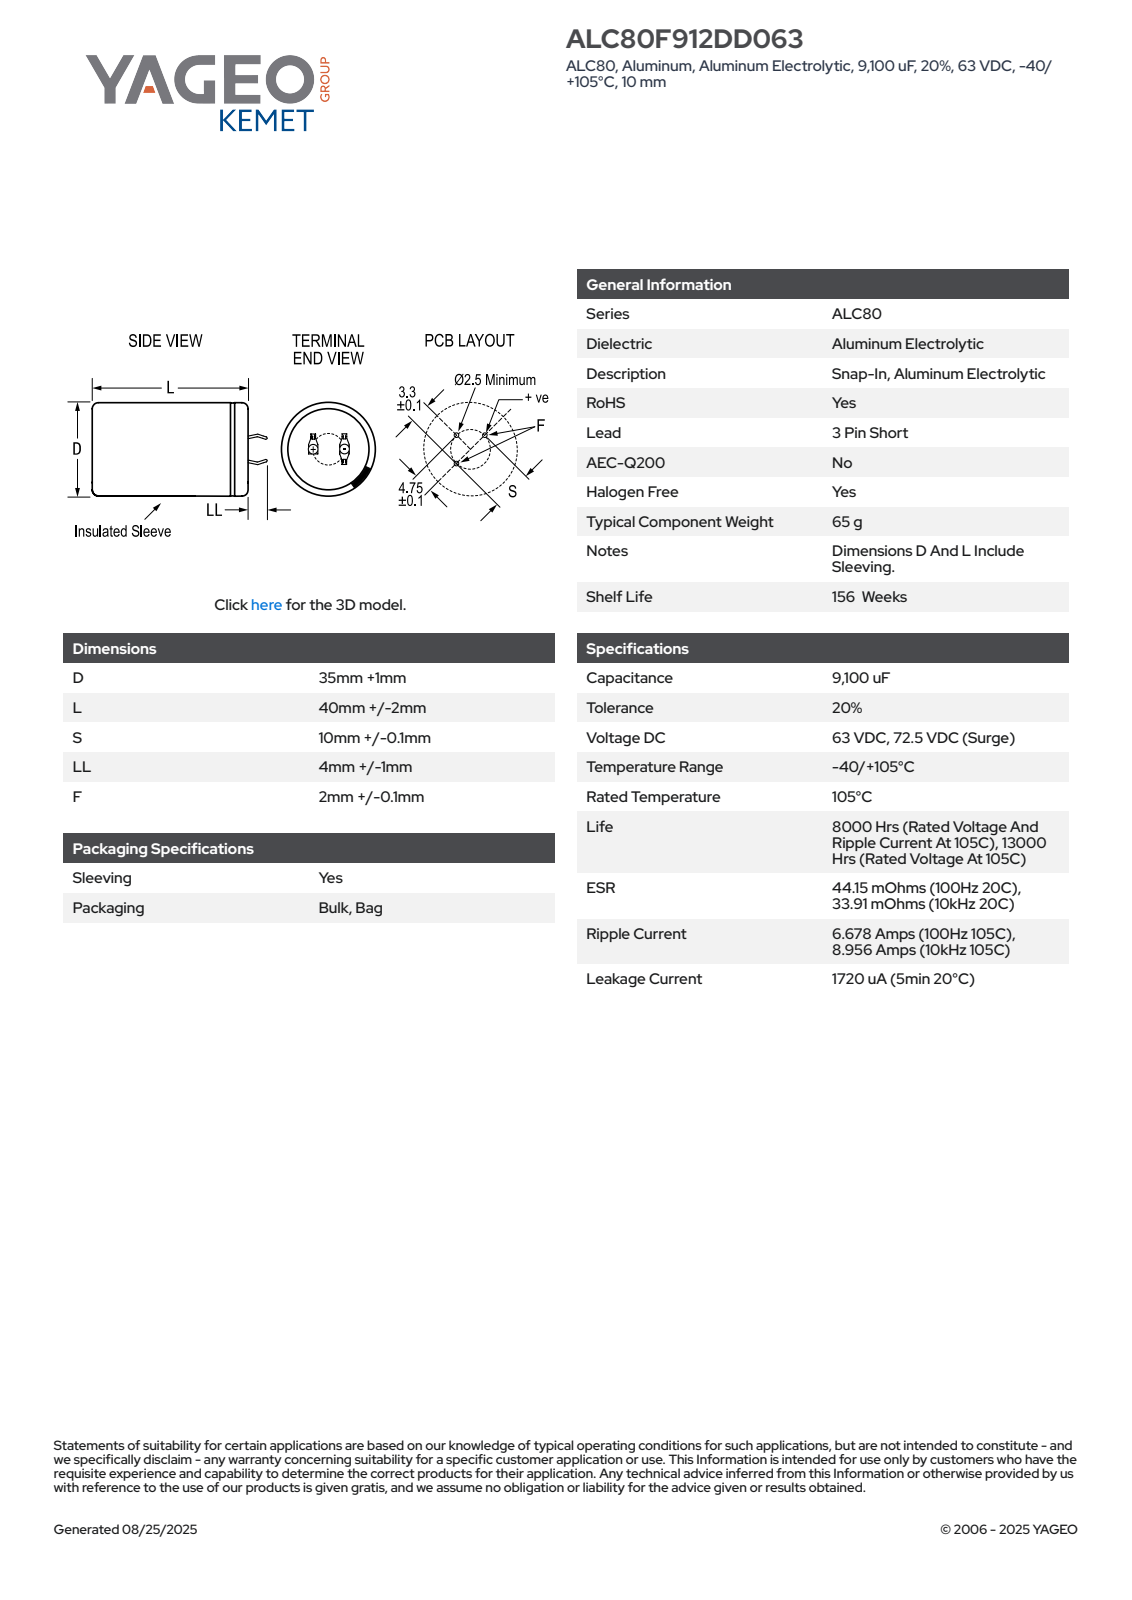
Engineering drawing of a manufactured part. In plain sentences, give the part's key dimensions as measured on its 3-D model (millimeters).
The part is named "CARS_K3P_35X40_D36L42S10LL5F2.1". Its 3-D file was written by "SolidWorks 2014 (AUTOMOTIVE_DESIGN)". It is 1 solid with 115 faces: 61 planar, 15 cylindrical and 39 other. Overall it measures 46.99 by 36 by 36 millimeters. Its volume is 42 223 cubic millimeters and its surface area 6 783 square millimeters. Round holes: 1 of diameter 31.85. Round bosses or shafts: 1 of diameter 36. Partial cylindrical surfaces (rounded edges, fillets, slot ends): 1 of radius 17.99. The main face-to-face distances are 41.99, 42.49, 0.5, 0.6, 8.22, 0.59, 0.75, 1.35, 6.51, 2.1.
